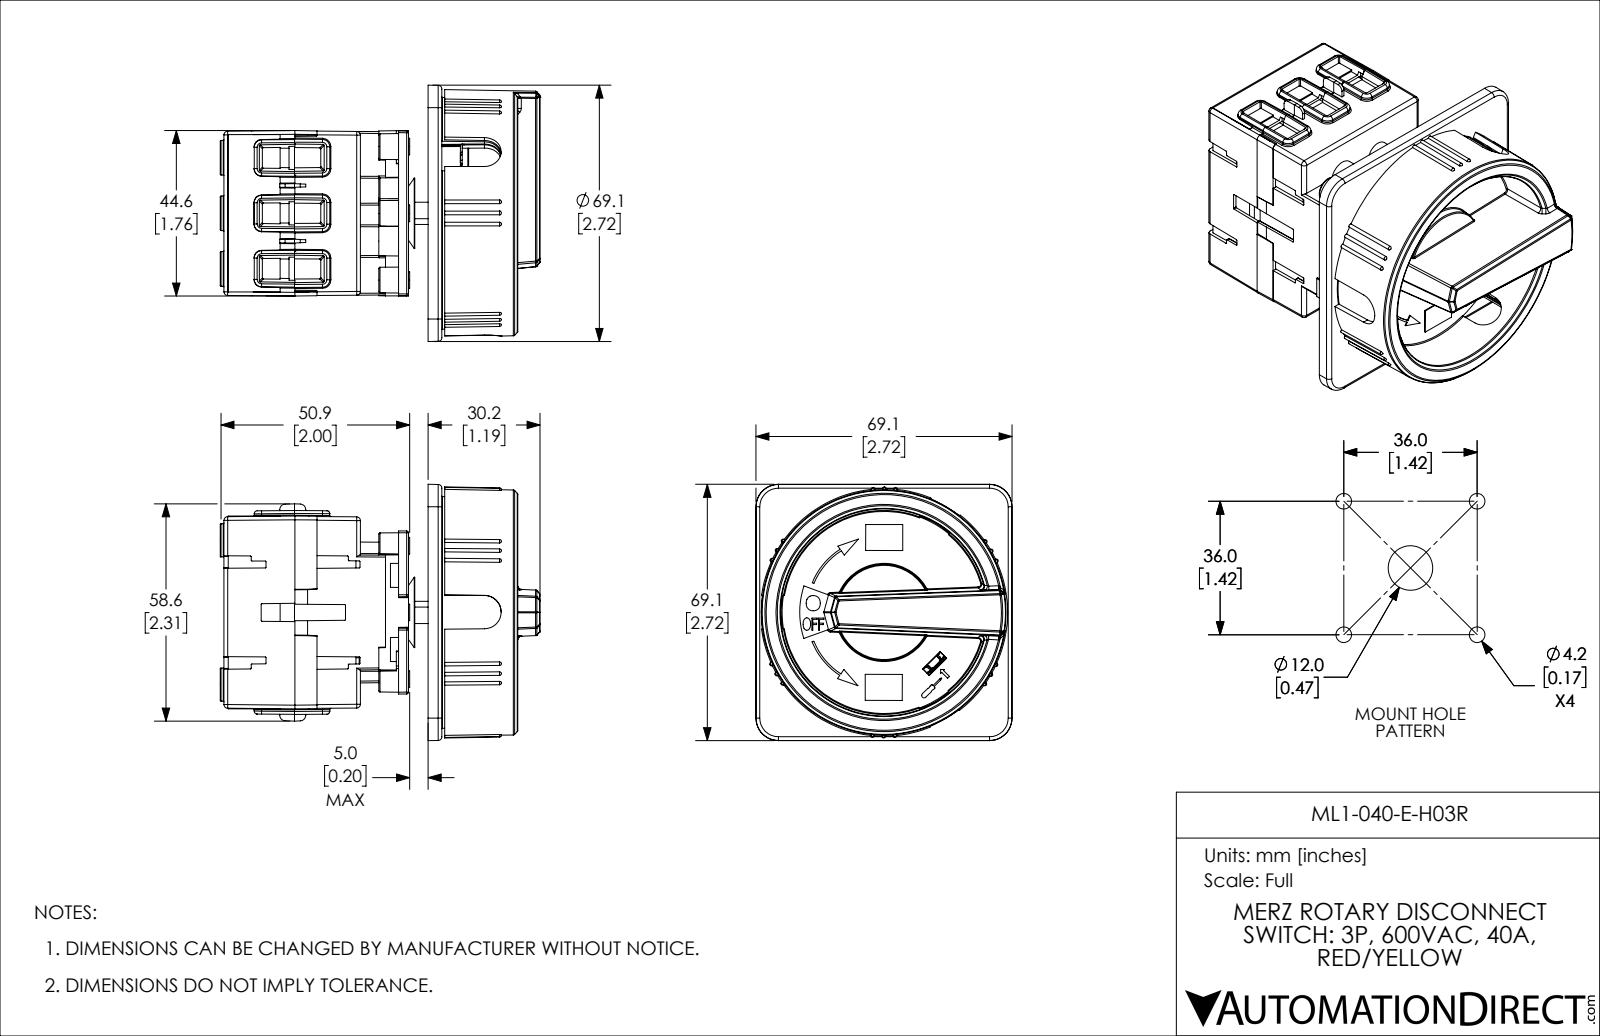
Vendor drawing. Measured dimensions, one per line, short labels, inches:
name: ML1-040-E-H03R
written by: SolidWorks 2019 (AUTOMOTIVE_DESIGN)
unit: in
bodies: 1 solid, 2964 faces (1185 planar, 610 cylindrical, 1169 other)
size: 3.398 × 2.722 × 2.722
volume: 8.361 in³; area: 101.4 in²
bosses: 2× ⌀0.071, 1× ⌀0.748, 1× ⌀0.236
rounds: 132× R0.02, 68× R0.012, 50× R0.039, 44× R0.008, 41× R0.008, 39× R0.01, 34× R0.031, 12× R0.079
face distances: 0.059, 0.138, 0.197, 0.079, 0.276, 0.571, 0.02, 0.551, 0.295, 0.807
